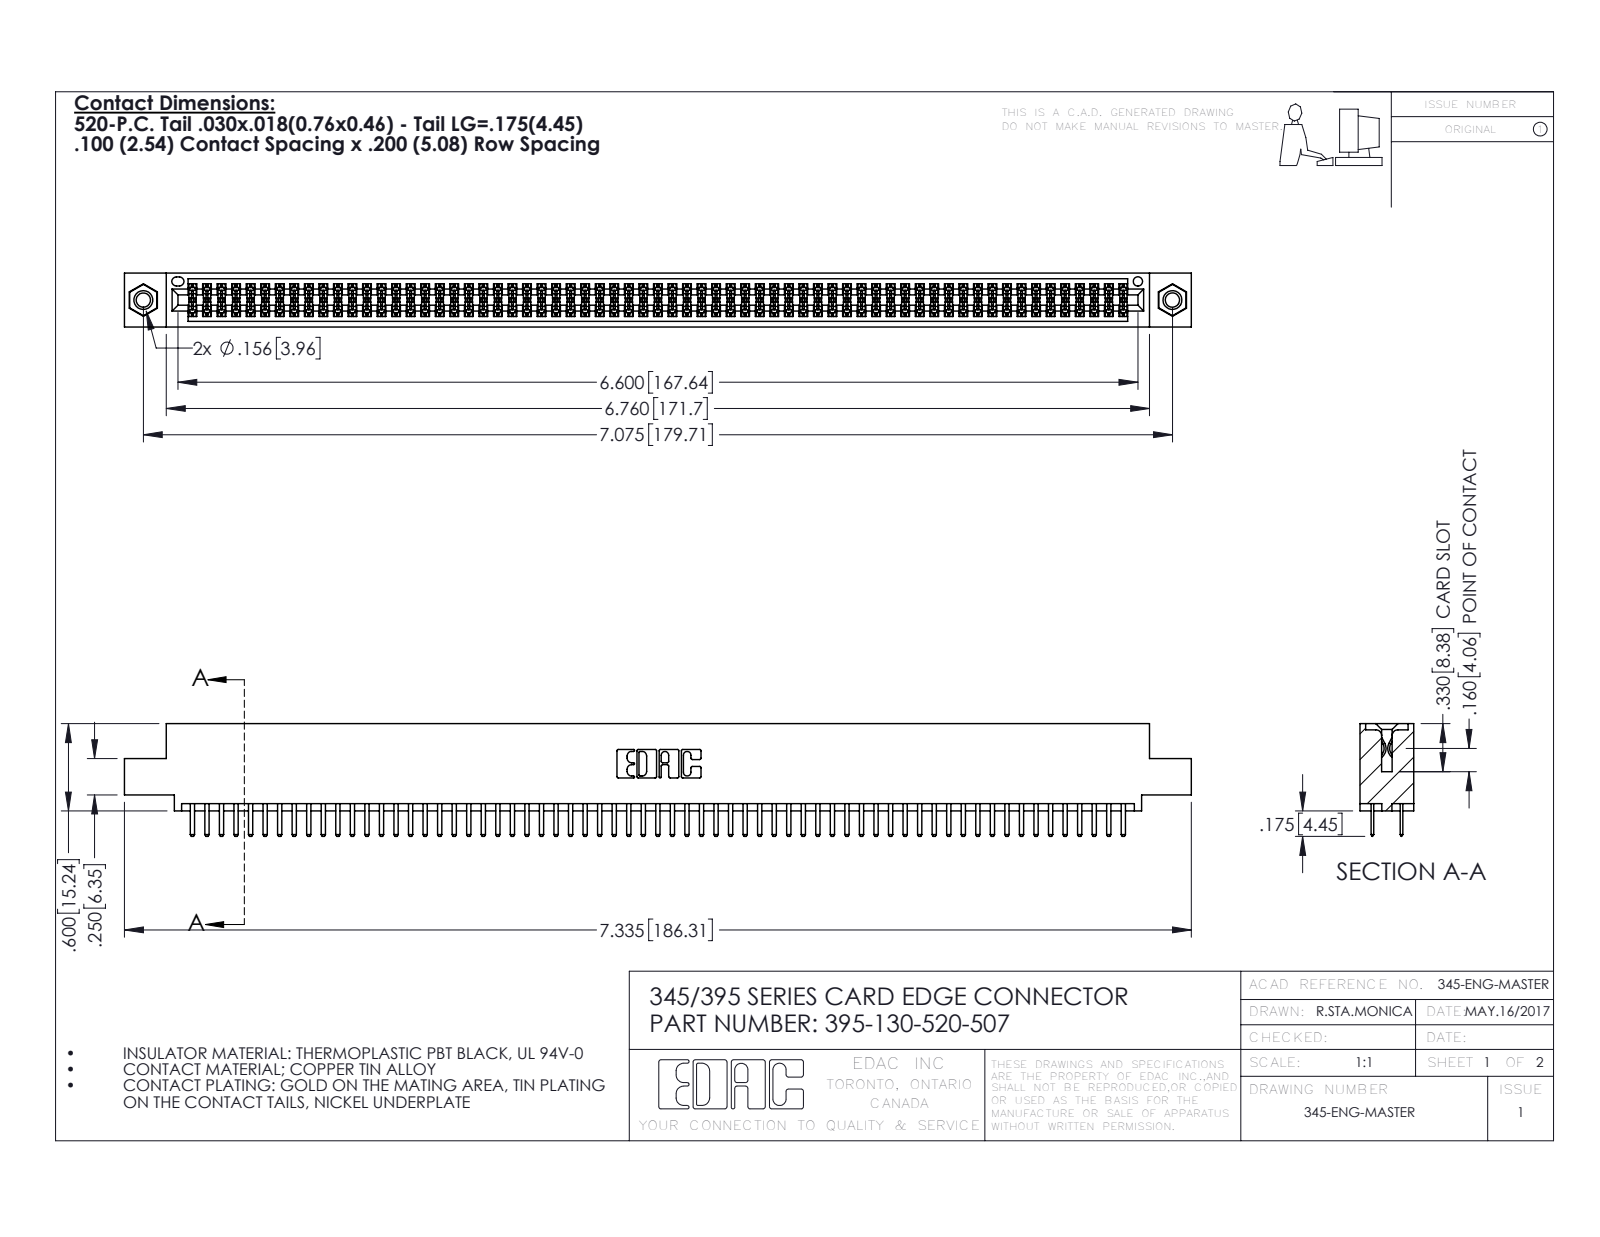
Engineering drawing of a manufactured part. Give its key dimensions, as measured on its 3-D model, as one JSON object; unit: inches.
{"part_name": "345 Part_0.110 Offset - 0.156 Dia-TI; 395-130-520-507; 345-250-001_345-250-005-103; 345-292-001_345-293-120", "step_written_by": "SolidWorks 2016 (CONFIG_CONTROL_DESIGN)", "units": "inches", "bodies": {"solids": 133, "faces": 7210, "planar": 4666, "cylindrical": 2528, "other": 16}, "overall_size": [7.335, 0.775, 0.37], "volume_in3": 1.109, "surface_area_in2": 42.31, "round_holes": [[0.098, 2], [0.125, 2], [0.156, 2], [0.064, 1]], "round_bosses_or_shafts": [[0.155, 2]], "partial_cylinders_radius": [[0.006, 195], [0.01, 134], [0.01, 22], [0.007, 6], [0.031, 6], [0.026, 3], [0.014, 2], [0.019, 2]], "face_to_face_distances": [0.072, 0.298, 0.2, 0.37, 0.098, 0.272, 0.025, 0.225, 0.022, 0.072], "hole_center_spacings": [0.27, 6.839, 7.075]}
